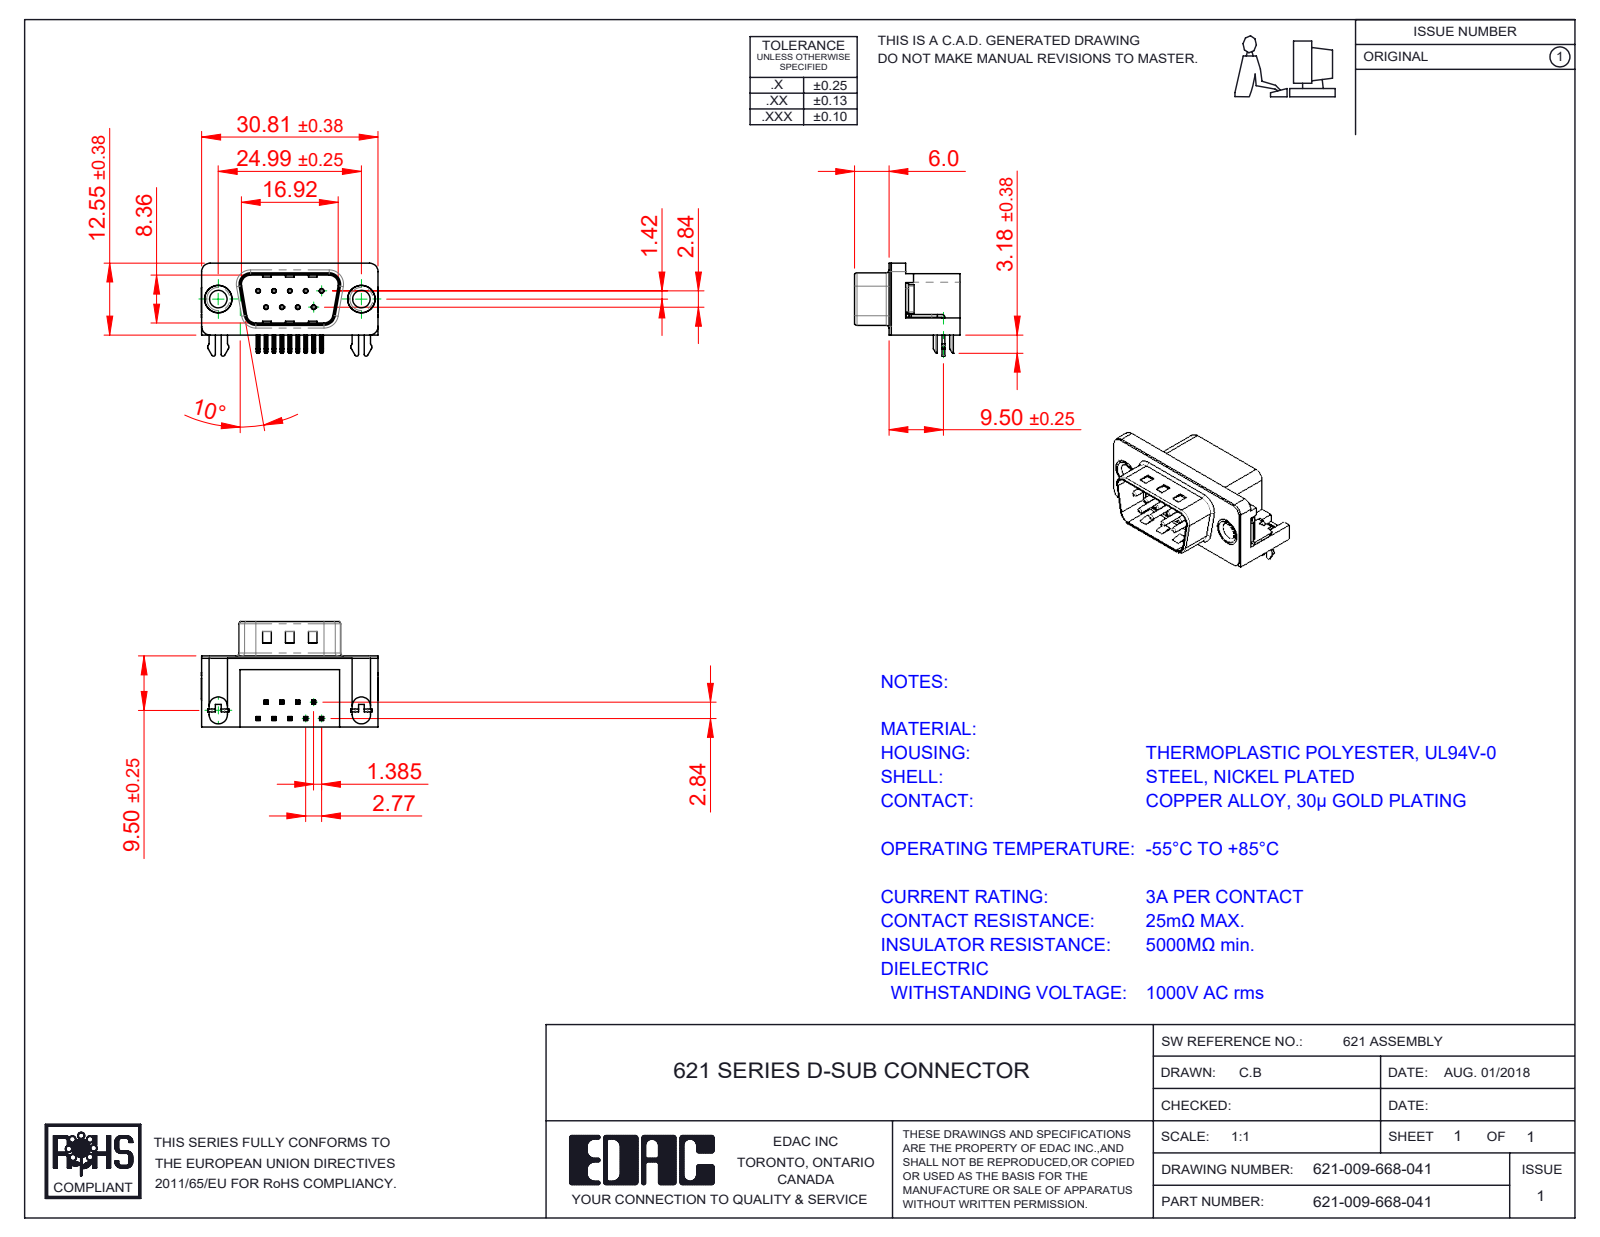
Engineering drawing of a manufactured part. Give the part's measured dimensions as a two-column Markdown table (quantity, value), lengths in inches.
| quantity | value |
| --- | --- |
| part name | 621 4 Prong Board Lock; 621 Contact Bottom; 621-009-668-041; 621 Thru Hole Rivet (+3 more) |
| STEP written by | SolidWorks 2016 (CONFIG_CONTROL_DESIGN) |
| units | inches |
| bodies | 15 solids, 1071 faces (615 planar, 303 cylindrical, 153 other) |
| overall size | 1.216 × 0.724 × 0.64 |
| volume | 0.198 in³ |
| surface area | 6.932 in² |
| round holes (diameter × count) | 0.014 × 9, 0.031 × 9, 0.079 × 2, 0.12 × 2, 0.157 × 2, 0.189 × 2, 0.197 × 2 |
| round bosses / shafts (diameter × count) | 0.03 × 9, 0.193 × 2, 0.187 × 2, 0.152 × 2, 0.118 × 2 |
| partial cylindrical surfaces (radius × count) | 0.01 × 48, 0.005 × 18, 0.039 × 16, 0.02 × 9, 0.059 × 8, 0.063 × 8, 0.035 × 4, 0.079 × 4 |
| main face-to-face distances | 0.016, 0.472, 0.488, 0.407, 0.114, 0.374, 0.098, 0.083, 0.02, 0.014 |
| hole center spacings | 0.124, 0.109, 0.218, 0.198, 0.198, 0.327, 0.294, 0.295 |
